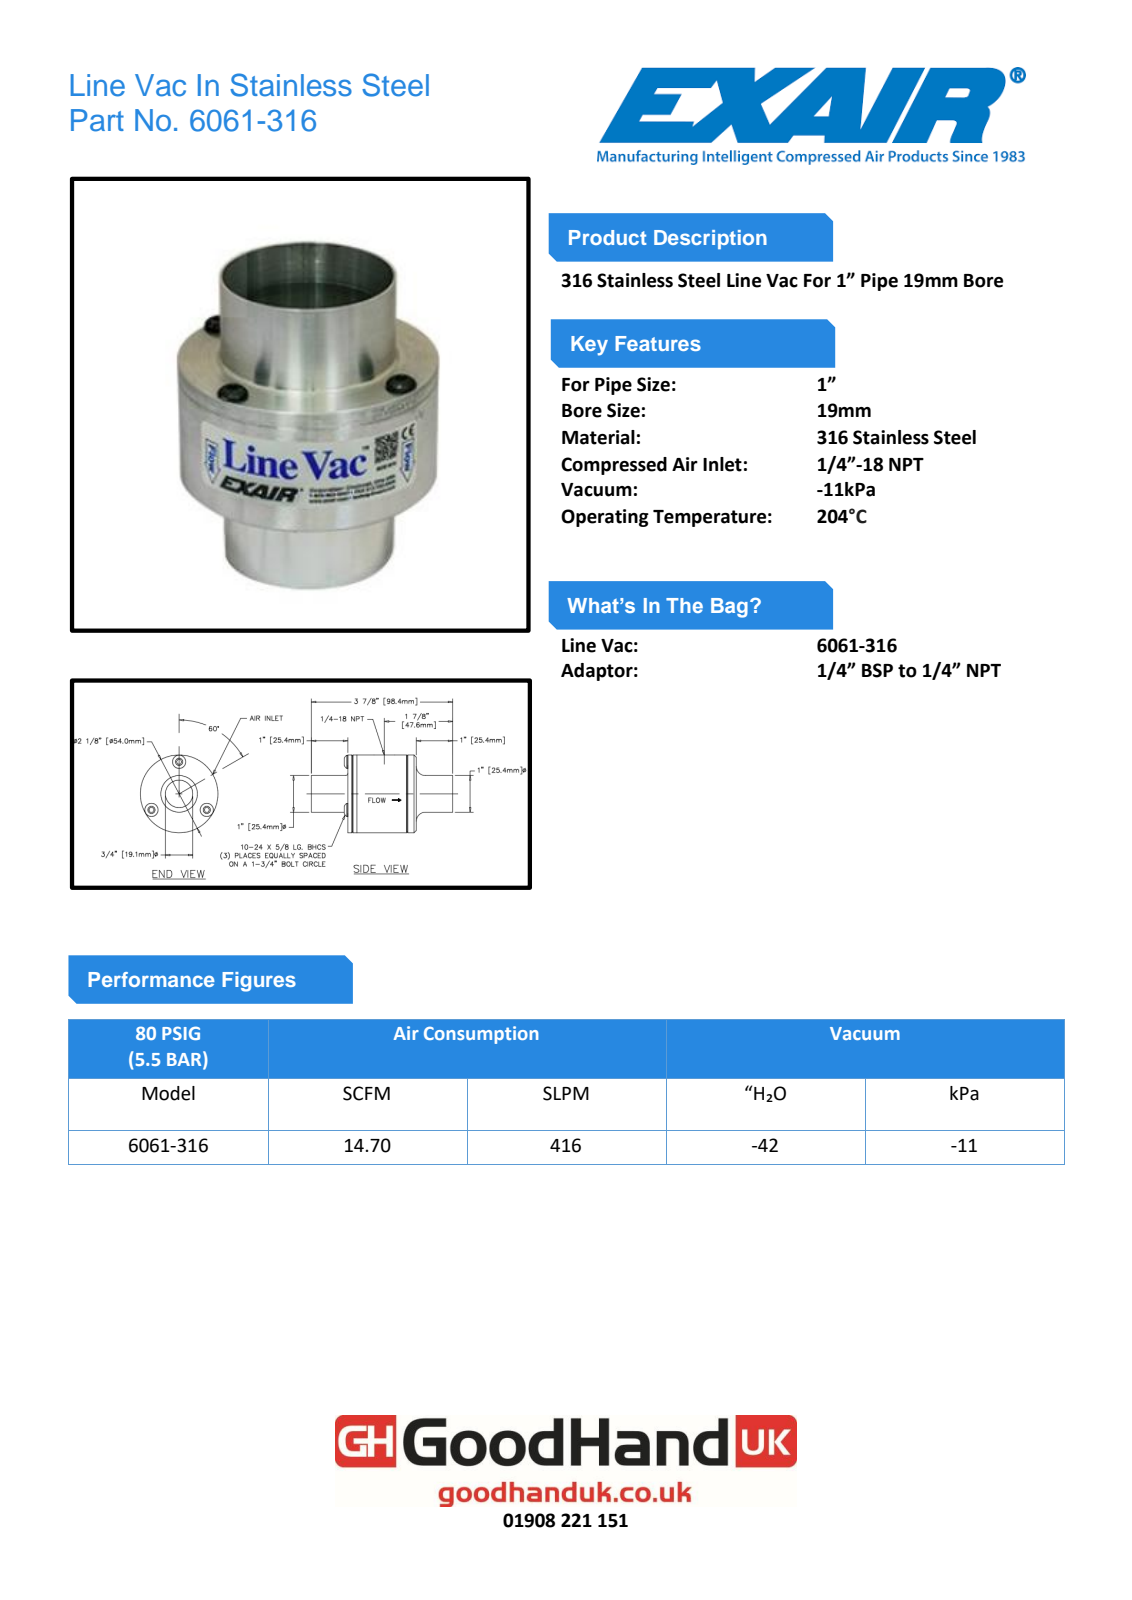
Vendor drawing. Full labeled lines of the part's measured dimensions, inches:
STEP written by: Autodesk Inventor 2010 (AUTOMOTIVE_DESIGN)
Units: inches
Bodies: 5 solids, 84 faces (42 planar, 24 cylindrical, 18 other)
Overall size (bounding box): 3.875 × 2.125 × 2.125
Volume: 6.304 in³ · Surface area: 44.97 in²
Round holes (diameter × count): ⌀0.152 ×3, ⌀0.186 ×3, ⌀0.218 ×3, ⌀0.438 ×1, ⌀0.75 ×1, ⌀1.4 ×1
Round bosses / shafts (diameter × count): ⌀0.361 ×3, ⌀0.19 ×3, ⌀2.125 ×1, ⌀1 ×1
Main face-to-face distances: 0.25, 0.375, 0.125, 1.625, 1.875, 1.5, 1, 2.875, 1.25, 2.625
Hole centre spacings: 1.515, 0.875, 0.874
